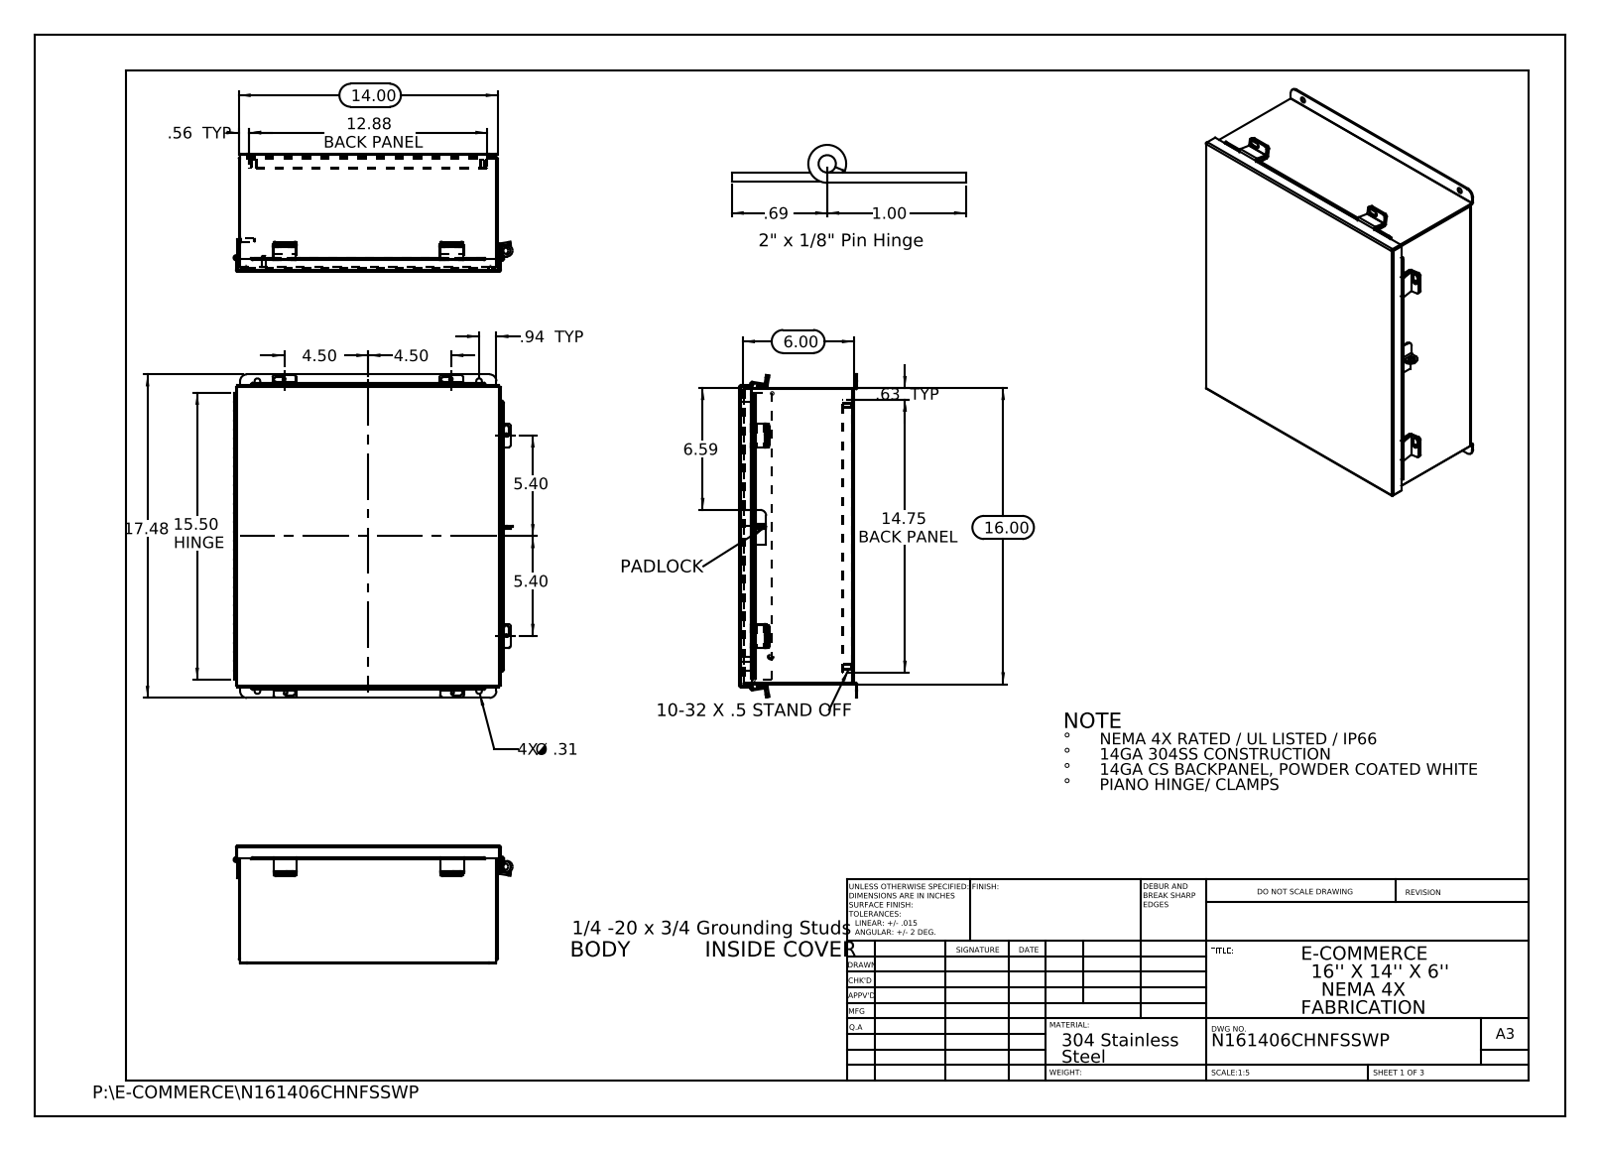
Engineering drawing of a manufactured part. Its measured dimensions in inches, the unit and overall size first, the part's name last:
Units: inches
Overall size (bounding box): 17.476 × 15.072 × 6.39
Round holes (diameter × count): ⌀0.25 ×10, ⌀0.187 ×4, ⌀0.312 ×4, ⌀0.125 ×1, ⌀0.125 ×1, ⌀0.373 ×1, ⌀0.375 ×1
Round bosses / shafts (diameter × count): ⌀0.313 ×4, ⌀0.315 ×2, ⌀0.236 ×2, ⌀0.273 ×1, ⌀0.25 ×1
Partial cylindrical surfaces — rounded edges, fillets, slot ends (radius × count): R0.125 ×21, R0.013 ×13, R0.009 ×12, R0.088 ×12, R0.133 ×12, R0.083 ×6, R0.1 ×6, R0.375 ×4
Main face-to-face distances: 0.075, 6.128, 6.053, 6.203, 0.074, 5.628, 0.575, 0.5, 5.553, 0.649
Hole centre spacings: 1.315, 12.244, 15.427, 19.652, 9, 11.976, 12.375, 14.126
Volume: 84.84 in³ · Surface area: 2 307 in²
Bodies: 27 solids, 866 faces (539 planar, 307 cylindrical, 20 other)
Part name (STEP PRODUCT): N161406CHNFSSWP Hinge Cover Side JIC; N161406CHNFSSWP JIC Top; HW-CLH-JH-20154; N161406CHNFSSWP JIC Enclosure Template (+8 more)
STEP written by: SolidWorks 2013 (CONFIG_CONTROL_DESIGN)
